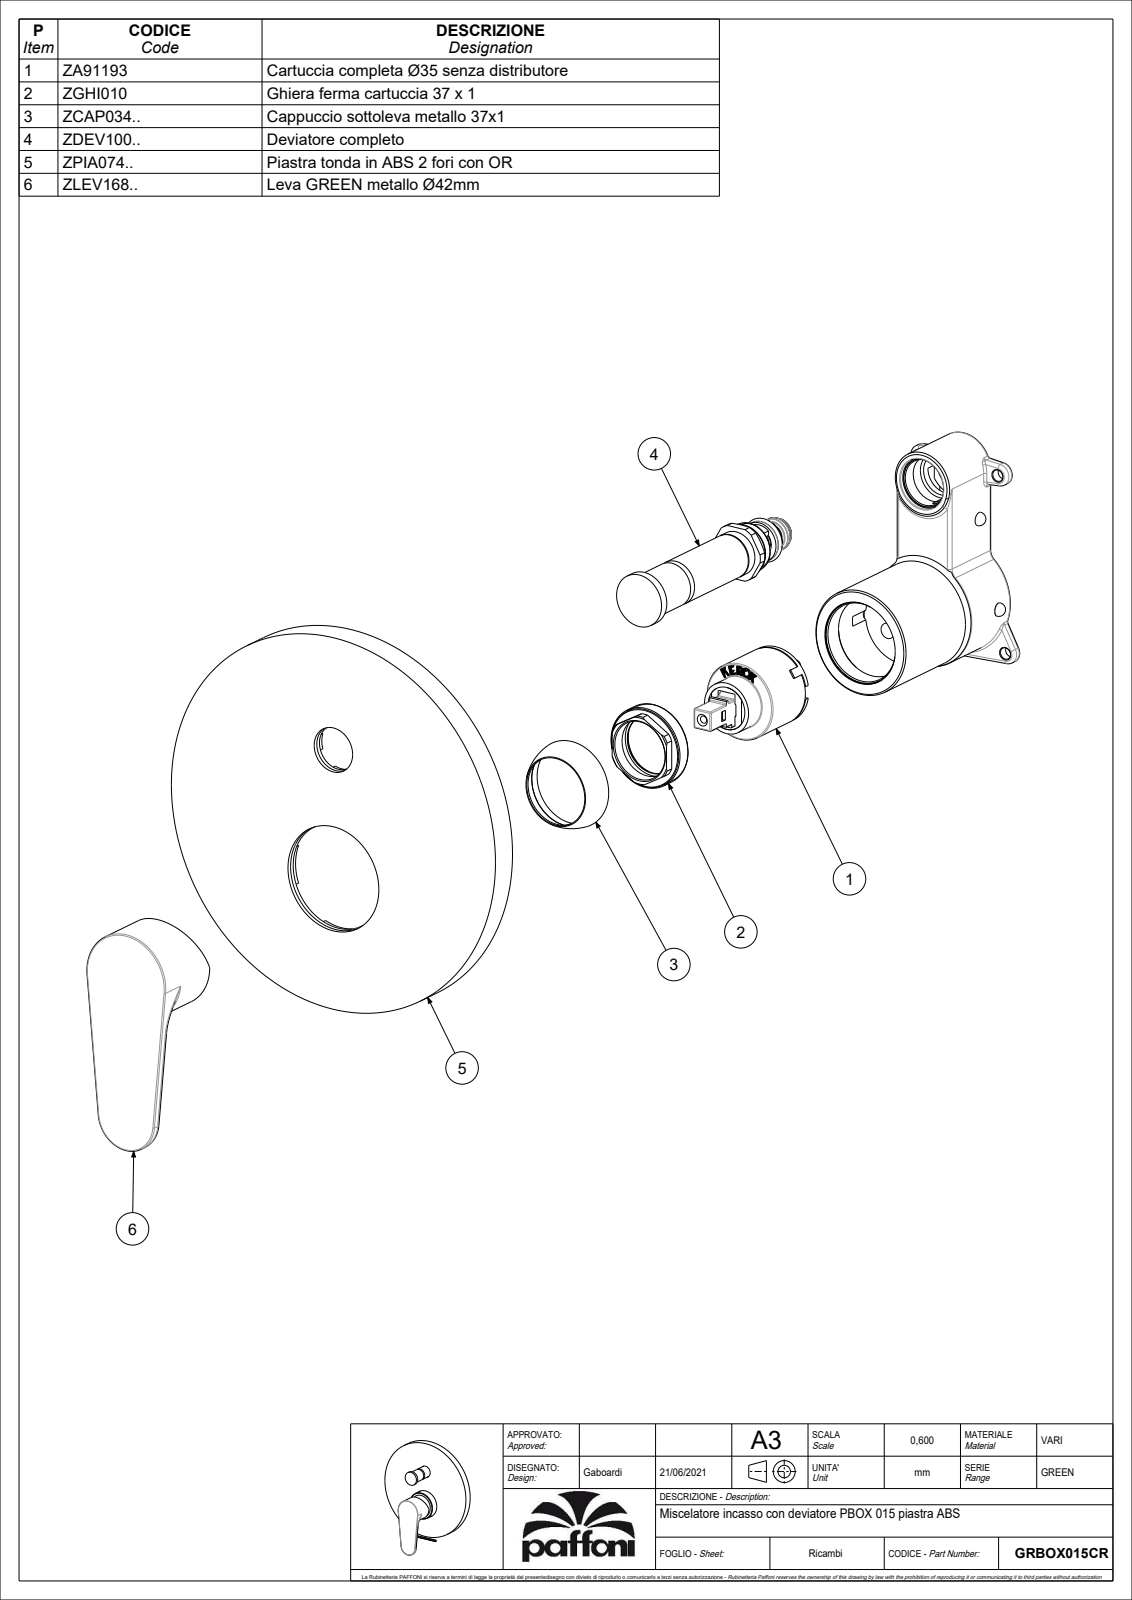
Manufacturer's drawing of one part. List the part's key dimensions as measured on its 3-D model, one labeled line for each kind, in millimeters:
Part name (STEP PRODUCT): GRBOX015CR
STEP written by: CREO PARAMETRIC BY PTC INC, 2020044 (CONFIG_CONTROL_DESIGN)
Units: millimetres
Bodies: 2 solids, 137 faces (49 planar, 53 cylindrical, 35 other)
Overall size (bounding box): 191.7 × 173 × 72.8
Volume: 362 014 mm³ · Surface area: 83 194 mm²
Round holes (diameter × count): ⌀3 ×1, ⌀4.2 ×1, ⌀30.6 ×1, ⌀36 ×1, ⌀37.5 ×1, ⌀39 ×1
Round bosses / shafts (diameter × count): ⌀173 ×1, ⌀48.1 ×1, ⌀42 ×1, ⌀24 ×1, ⌀20 ×1, ⌀15 ×1, ⌀7.6 ×1, ⌀5.5 ×1
Partial cylindrical surfaces — rounded edges, fillets, slot ends (radius × count): R0.5 ×2, R3 ×2, R2.5 ×1, R15 ×1
Main face-to-face distances: 13, 72.8, 59.8, 6, 53.8, 66.8, 2.5, 3.5, 70.3, 57.3
